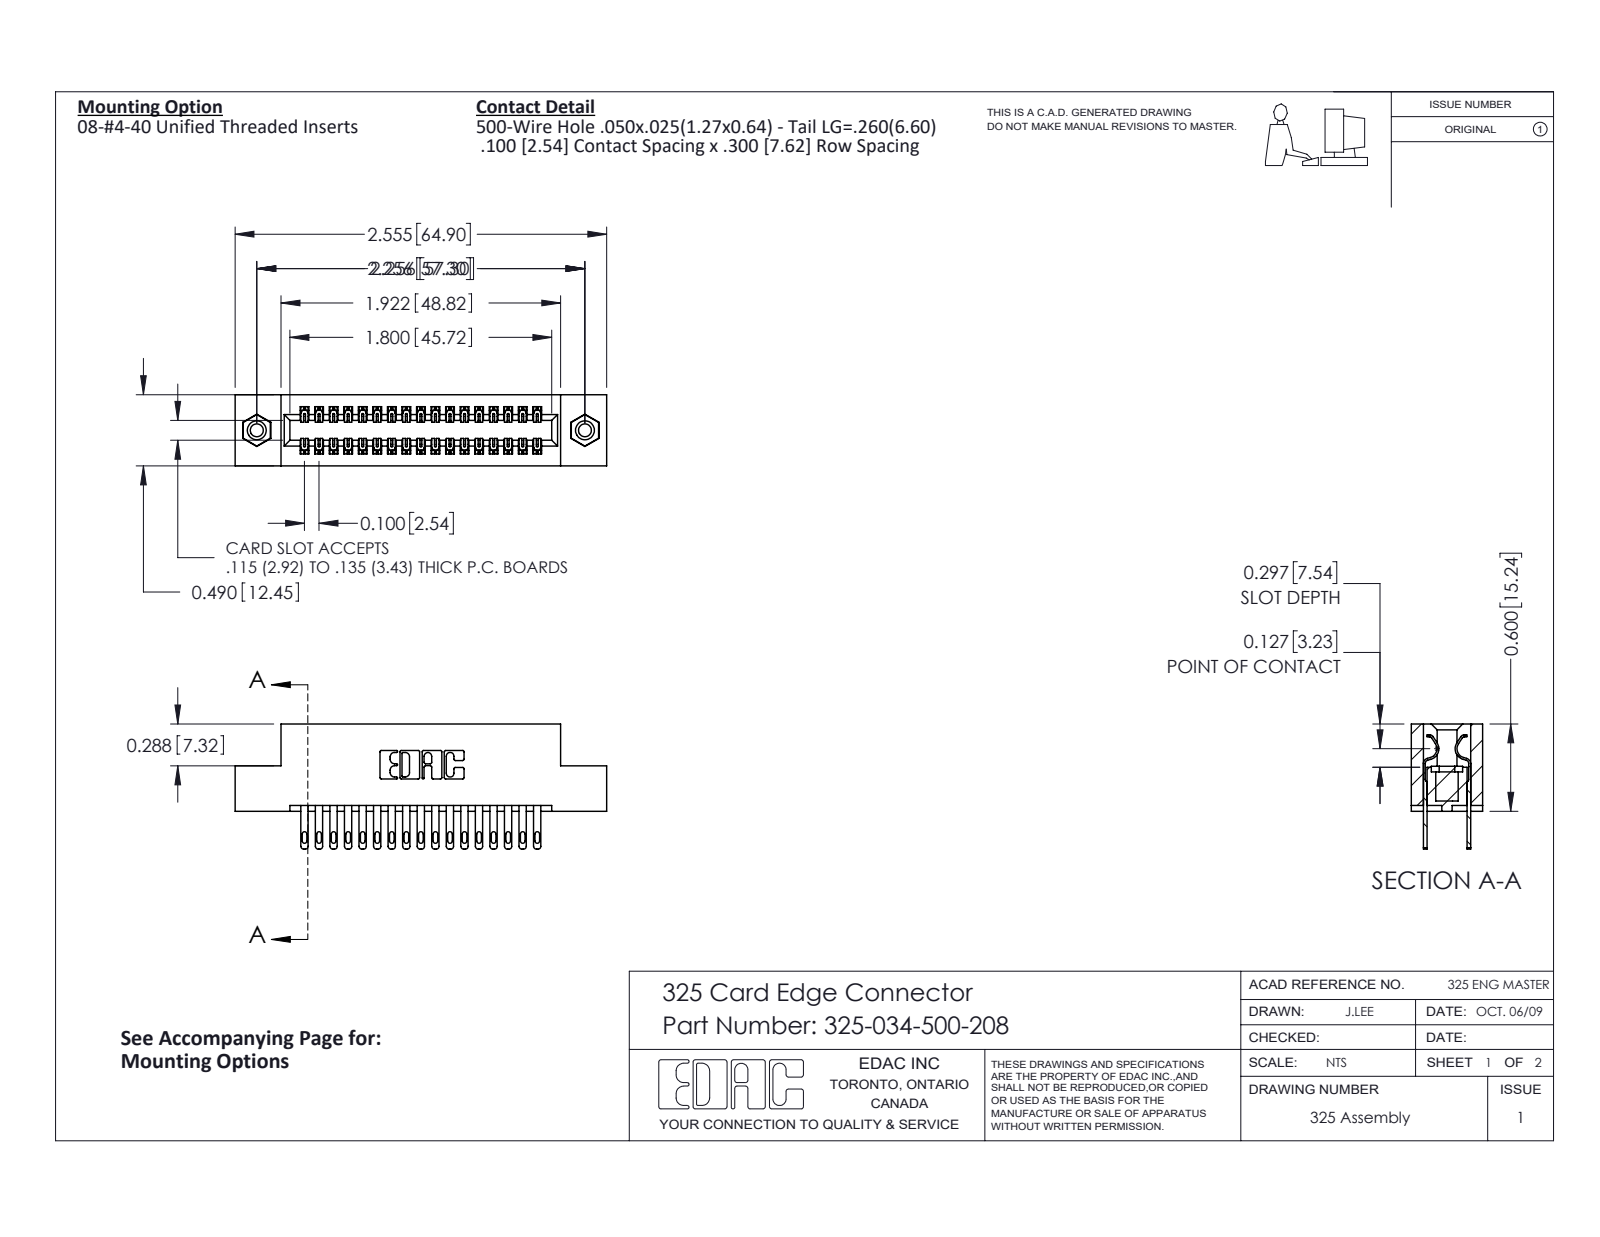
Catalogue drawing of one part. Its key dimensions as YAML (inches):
part_name: "325-292-001_325-293-100; 325-034-500-208; 325 Part_TI; 345-250-001_345-250-003-102"
step_written_by: "SolidWorks 2016 (CONFIG_CONTROL_DESIGN)"
units: inches
bodies: {solids: 37, faces: 1806, planar: 1122, cylindrical: 668, other: 16}
overall_size: [2.555, 0.86, 0.49]
volume: 0.504
surface_area: 15.13
round_holes:
  - {diameter: 0.089, count: 2}
  - {diameter: 0.125, count: 2}
  - {diameter: 0.16, count: 2}
round_bosses_or_shafts:
  - {diameter: 0.155, count: 2}
partial_cylinders:
  - {radius: 0.006, count: 51}
  - {radius: 0.016, count: 34}
  - {radius: 0.02, count: 34}
  - {radius: 0.01, count: 22}
  - {radius: 0.007, count: 6}
  - {radius: 0.031, count: 6}
  - {radius: 0.026, count: 3}
  - {radius: 0.014, count: 2}
face_to_face_distances: [0.083, 0.407, 0.3, 0.107, 0.383, 0.025, 0.49, 0.325, 0.6, 0.04]
hole_center_spacings: [2.256]
